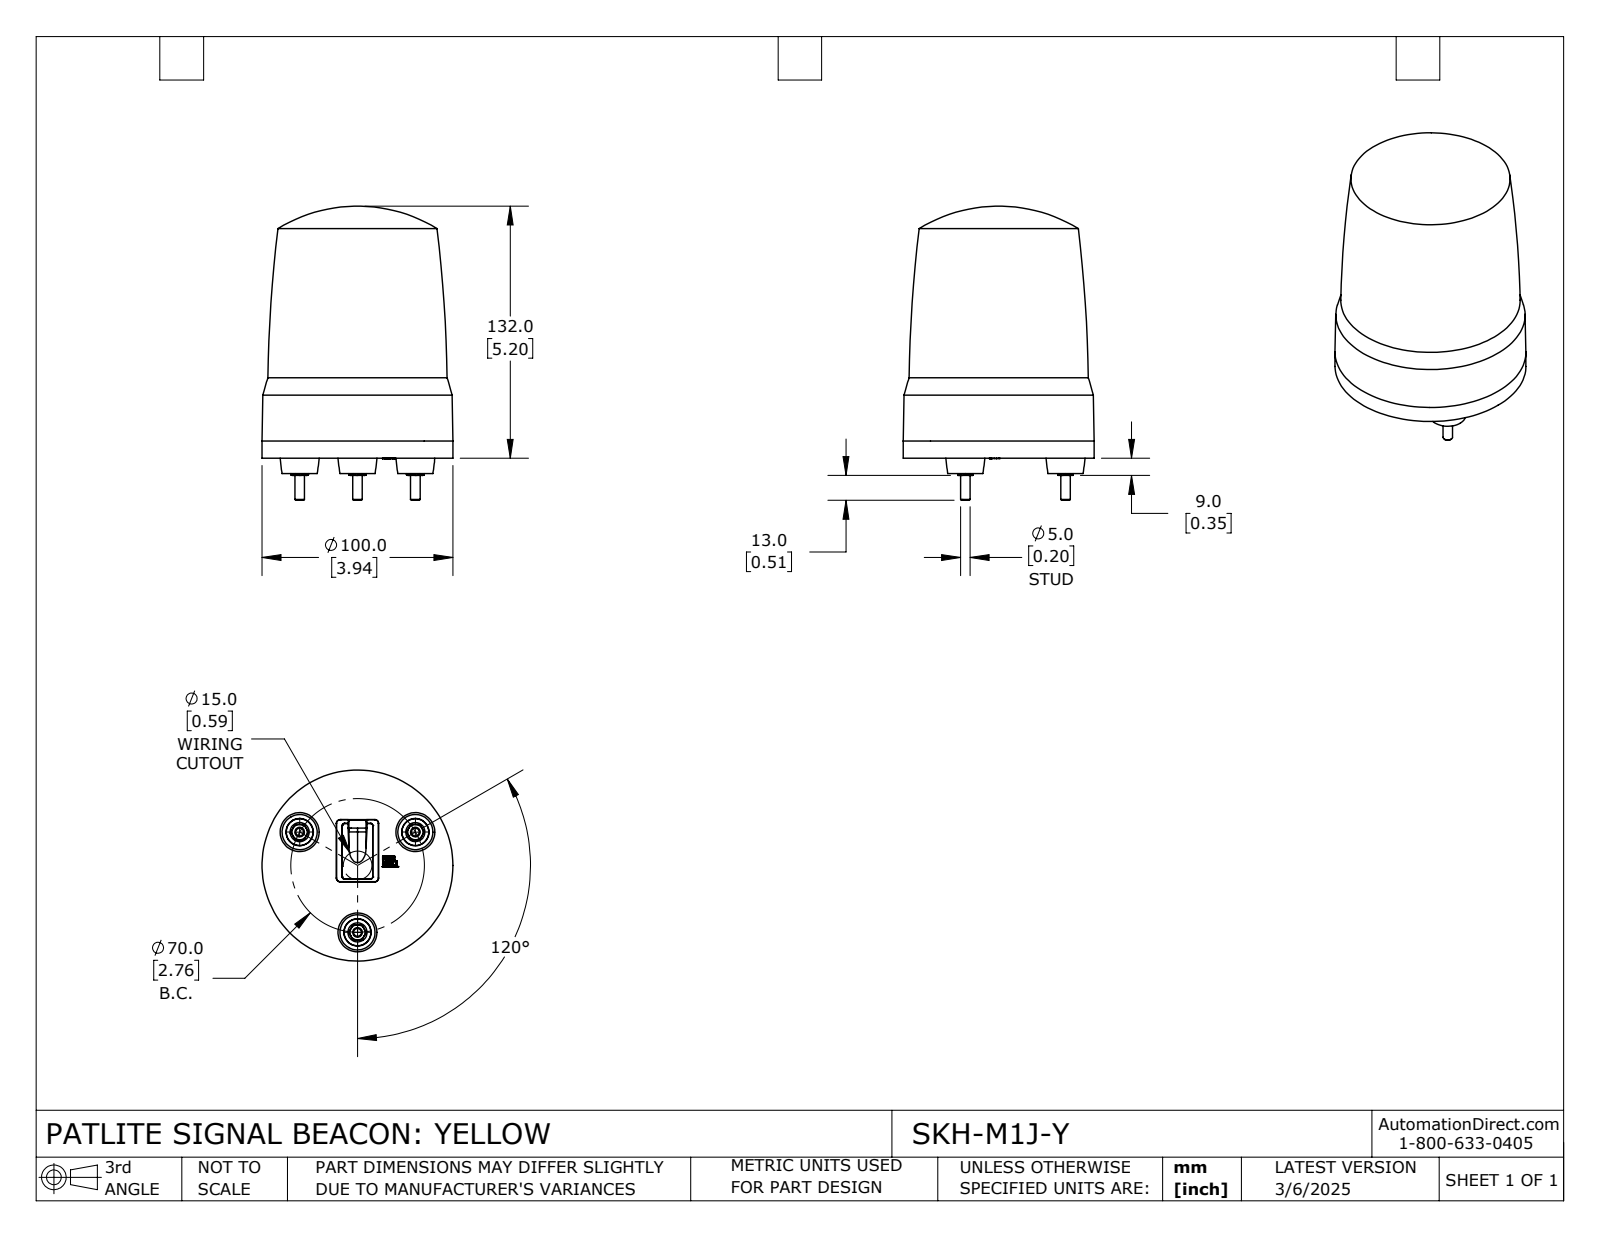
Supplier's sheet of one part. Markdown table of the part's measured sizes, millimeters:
| quantity | value |
| --- | --- |
| part name | SKH-M1J-Y |
| STEP written by | SolidWorks 2024 (CONFIG_CONTROL_DESIGN) |
| units | millimeters |
| bodies | 1 solid, 327 faces (159 planar, 14 cylindrical, 154 other) |
| overall size | 154 × 100 × 100 |
| volume | 859 960 mm³ |
| surface area | 52 586 mm² |
| round bosses / shafts (diameter × count) | 10 × 3, 5 × 3, 100 × 1 |
| main face-to-face distances | 8, 0.85, 8.85, 1.6, 10.45, 2.45, 3.8, 4.2, 5.05, 6.65 |
